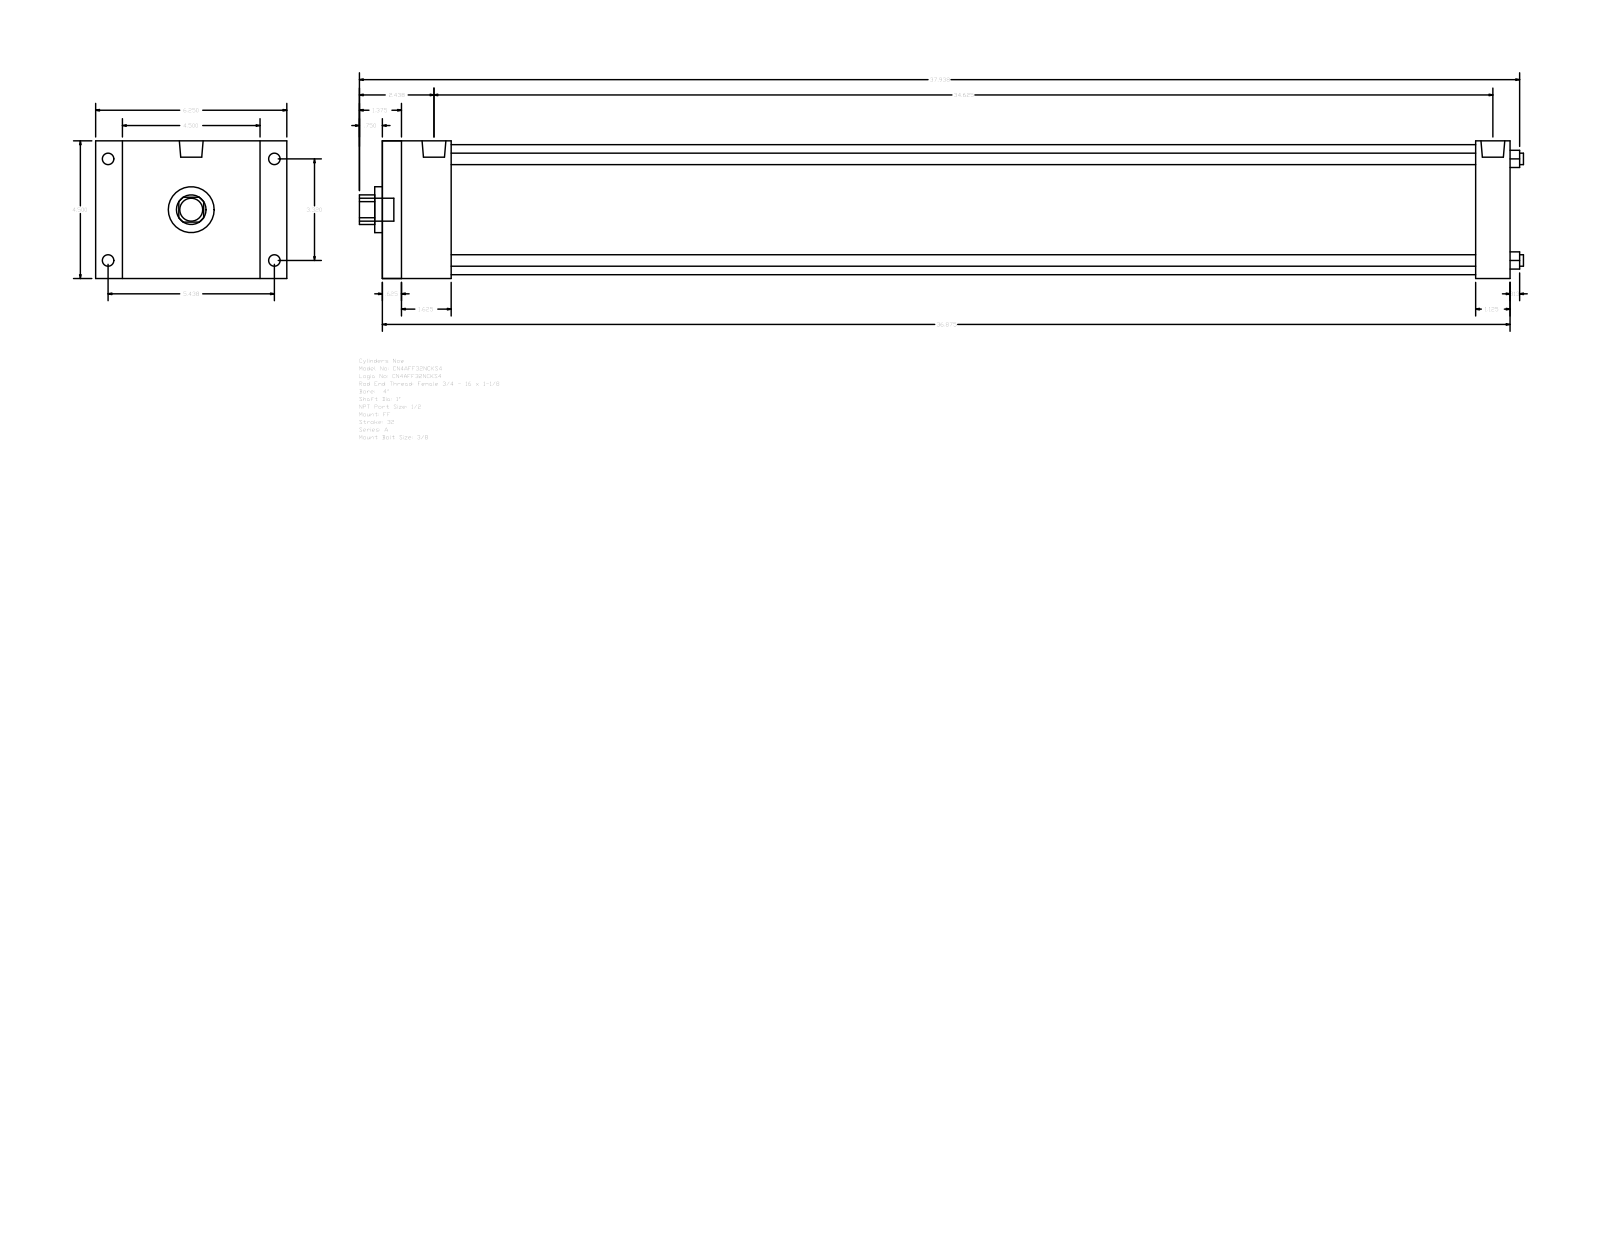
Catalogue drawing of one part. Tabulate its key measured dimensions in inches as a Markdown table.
| quantity | value |
| --- | --- |
| part name | A_FF__0400_1 |
| STEP written by | GSSL Pune (CONFIG_CONTROL_DESIGN) |
| units | inches |
| bodies | 0 solids, 92 faces (64 planar, 28 cylindrical, 0 other) |
| overall size | 38.063 × 6.25 × 4.5 |
| round holes (diameter × count) | 0.375 × 4, 1 × 1, 1.5 × 1, 4.25 × 1 |
| round bosses / shafts (diameter × count) | 0.375 × 4, 0.344 × 4, 0.778 × 2, 0.75 × 1 |
| partial cylindrical surfaces (radius × count) | 0.484 × 1 |
| main face-to-face distances | 4.5, 36.875, 0.625, 36.25, 1.125, 0.875, 5.375, 35.75, 35.125, 2.25 |
| hole center spacings | 2.347, 3.32, 4.695 |
